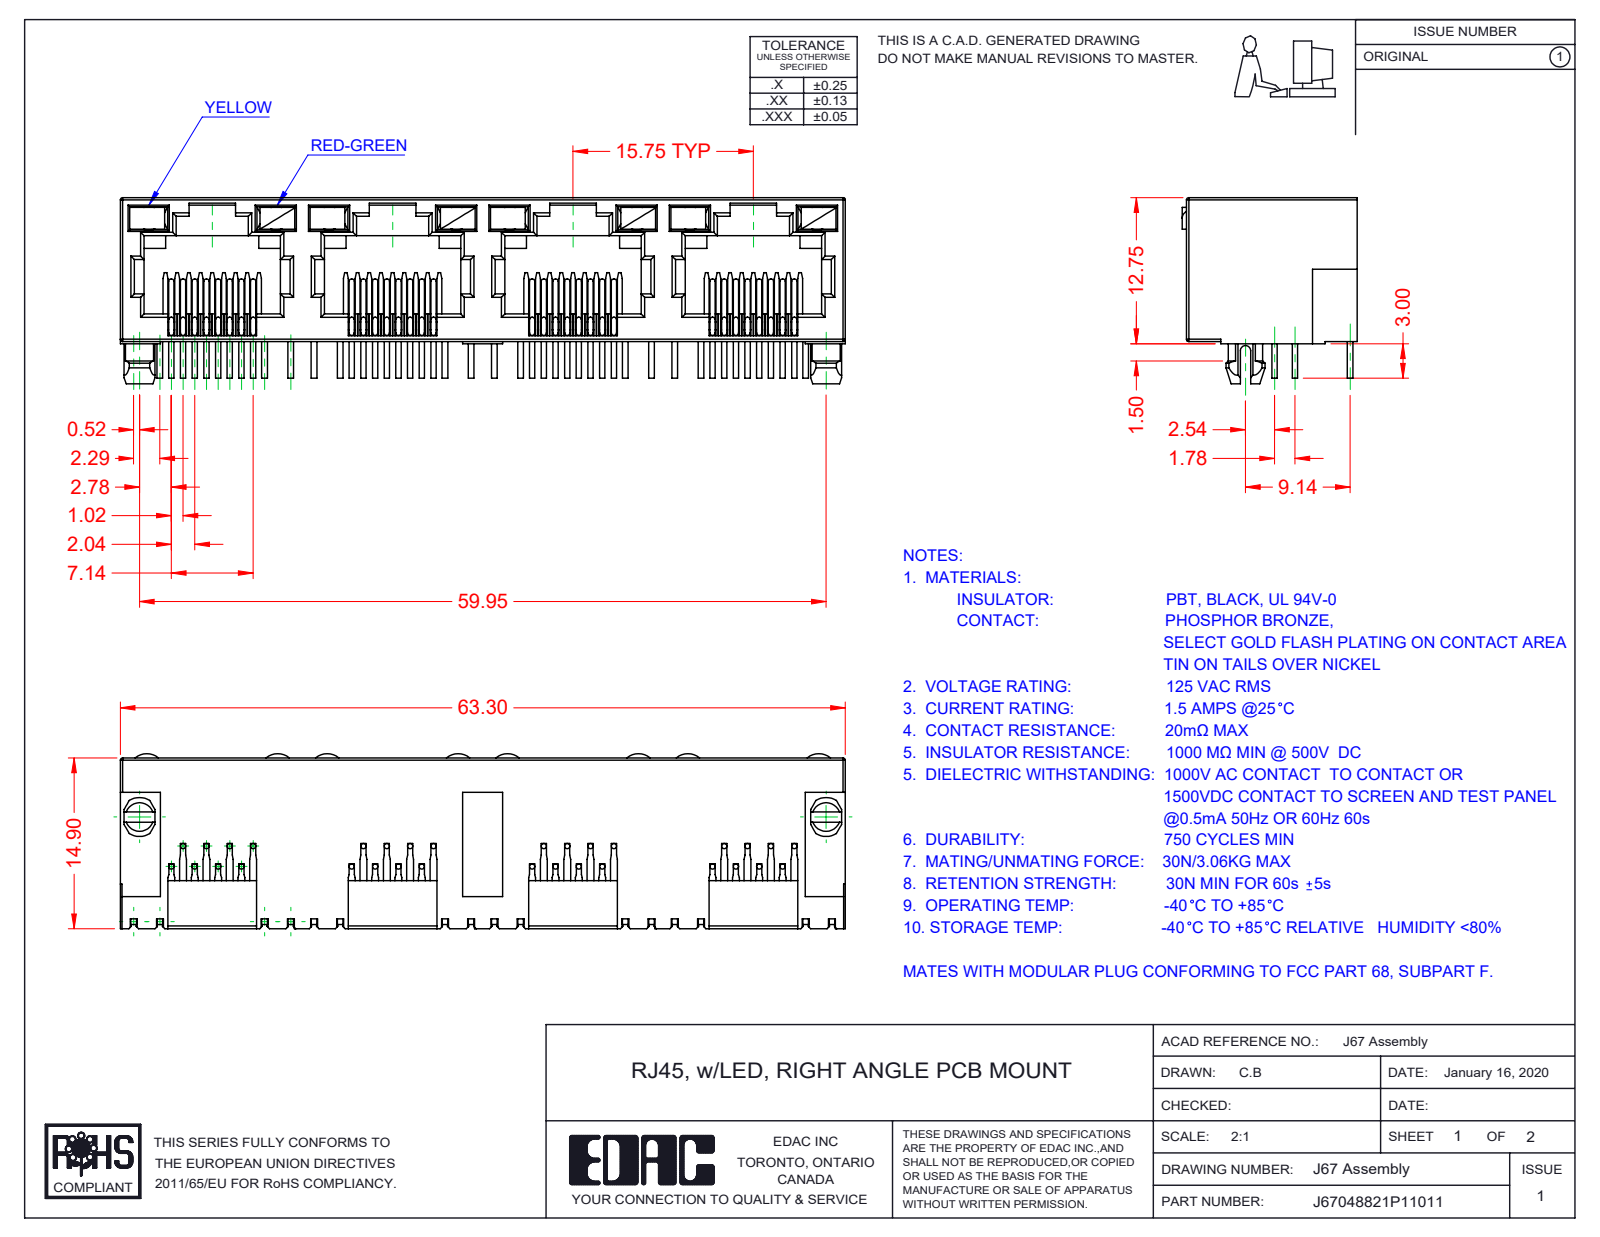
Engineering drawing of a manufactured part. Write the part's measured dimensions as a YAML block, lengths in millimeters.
part_name: "67 Contacts; J67048822P16011; 67 LED RH_6-Red-Green; 67 LED LH_1-Yellow (+1 more)"
step_written_by: "SolidWorks 2016 (CONFIG_CONTROL_DESIGN)"
units: millimeters
bodies: {solids: 41, faces: 2473, planar: 1781, cylindrical: 484, other: 208}
overall_size: [63.3, 16.25, 15.28]
volume: 5159
surface_area: 11573
round_bosses_or_shafts:
  - {diameter: 0.46, count: 96}
partial_cylinders:
  - {radius: 0.2, count: 66}
  - {radius: 0.3, count: 29}
  - {radius: 0.45, count: 9}
  - {radius: 1.55, count: 8}
  - {radius: 1.5, count: 2}
  - {radius: 1.7, count: 2}
  - {radius: 0.35, count: 1}
  - {radius: 1, count: 1}
face_to_face_distances: [0.5, 12.55, 1.89, 0.89, 10, 15.75, 1, 1.39, 11, 11.89]
